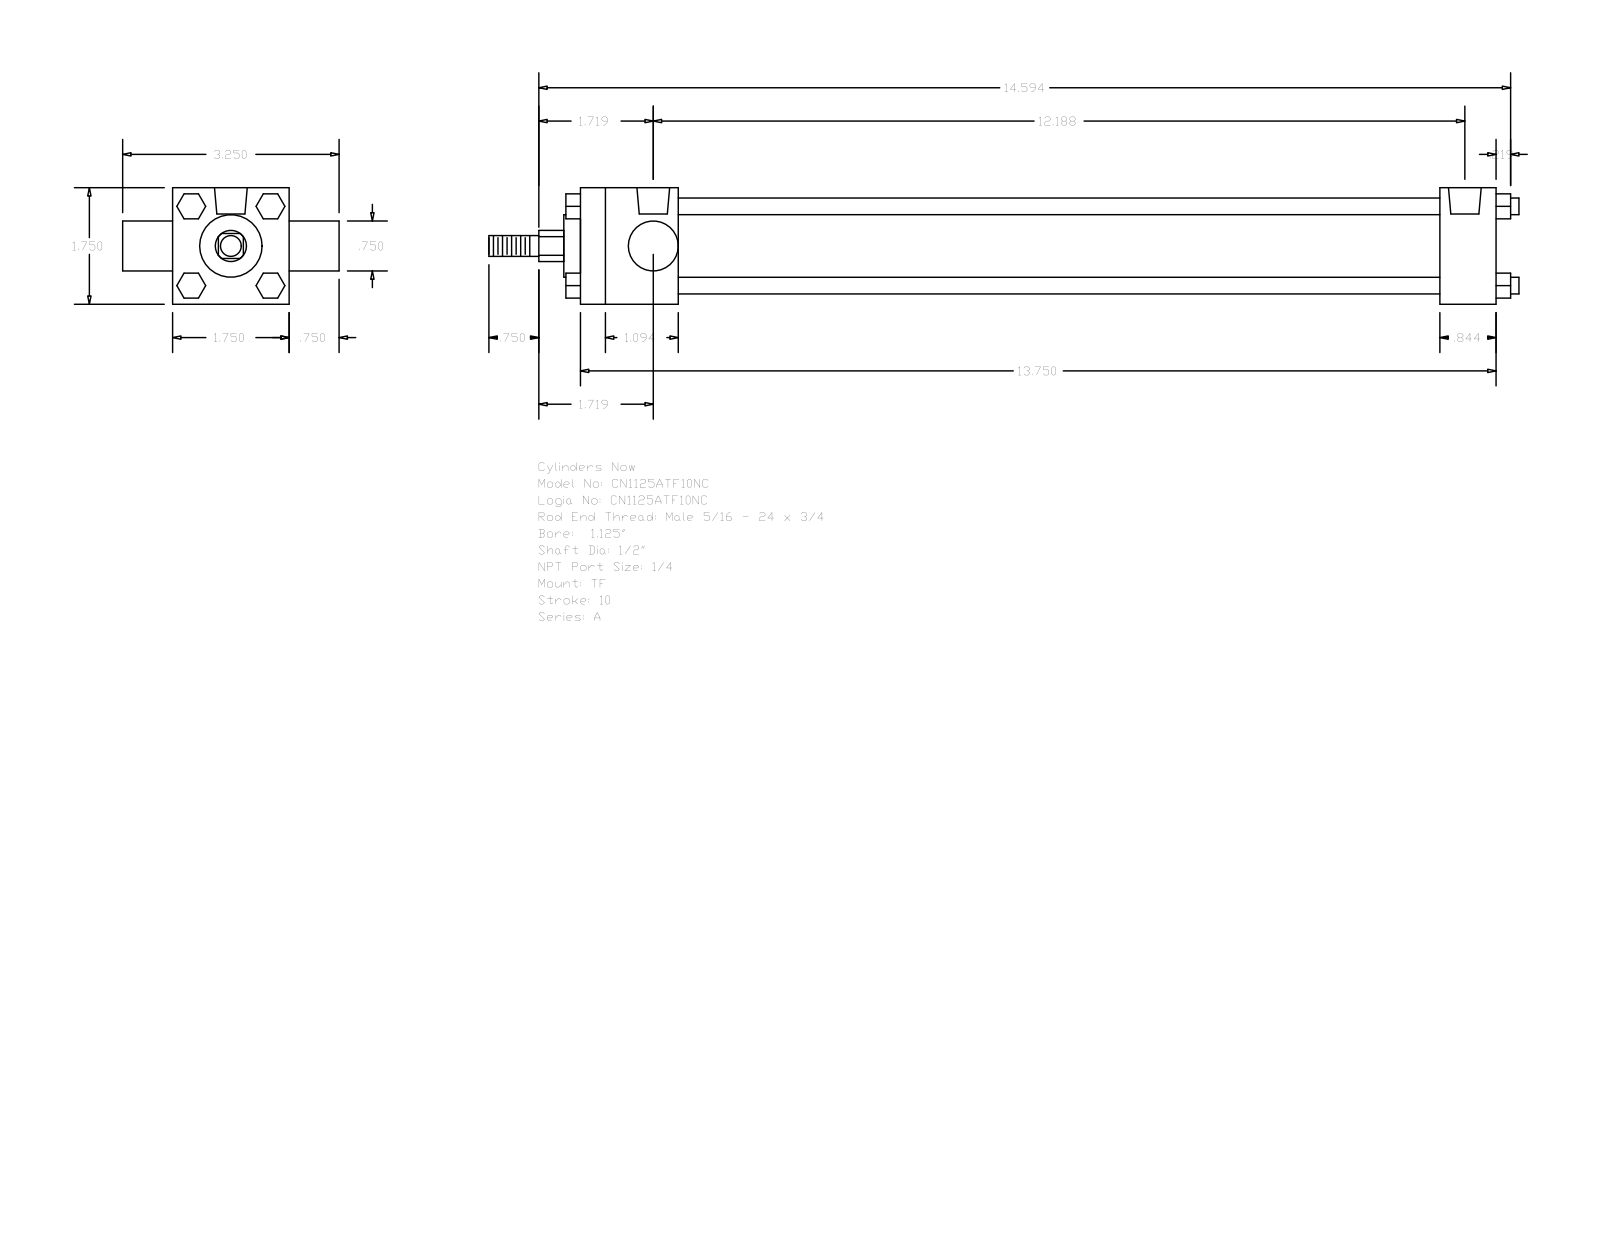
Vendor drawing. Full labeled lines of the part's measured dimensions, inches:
Part name (STEP PRODUCT): A_TF__0112_0.5
STEP written by: GSSL Pune (CONFIG_CONTROL_DESIGN)
Units: inches
Bodies: 0 solids, 120 faces (92 planar, 28 cylindrical, 0 other)
Overall size (bounding box): 15.469 × 3.25 × 1.75
Round holes (diameter × count): ⌀0.219 ×3, ⌀0.492 ×2
Round bosses / shafts (diameter × count): ⌀0.25 ×4, ⌀1.255 ×1, ⌀0.937 ×1, ⌀0.75 ×1, ⌀0.5 ×1, ⌀0.313 ×1
Partial cylindrical surfaces — rounded edges, fillets, slot ends (radius × count): R0.234 ×1
Main face-to-face distances: 1.75, 13.75, 12.906, 0.844, 1.469, 11.437, 12.281, 0.75, 2.5, 0.375
Hole centre spacings: 0.062, 0.063, 12.063, 12.125, 12.125, 12.187
